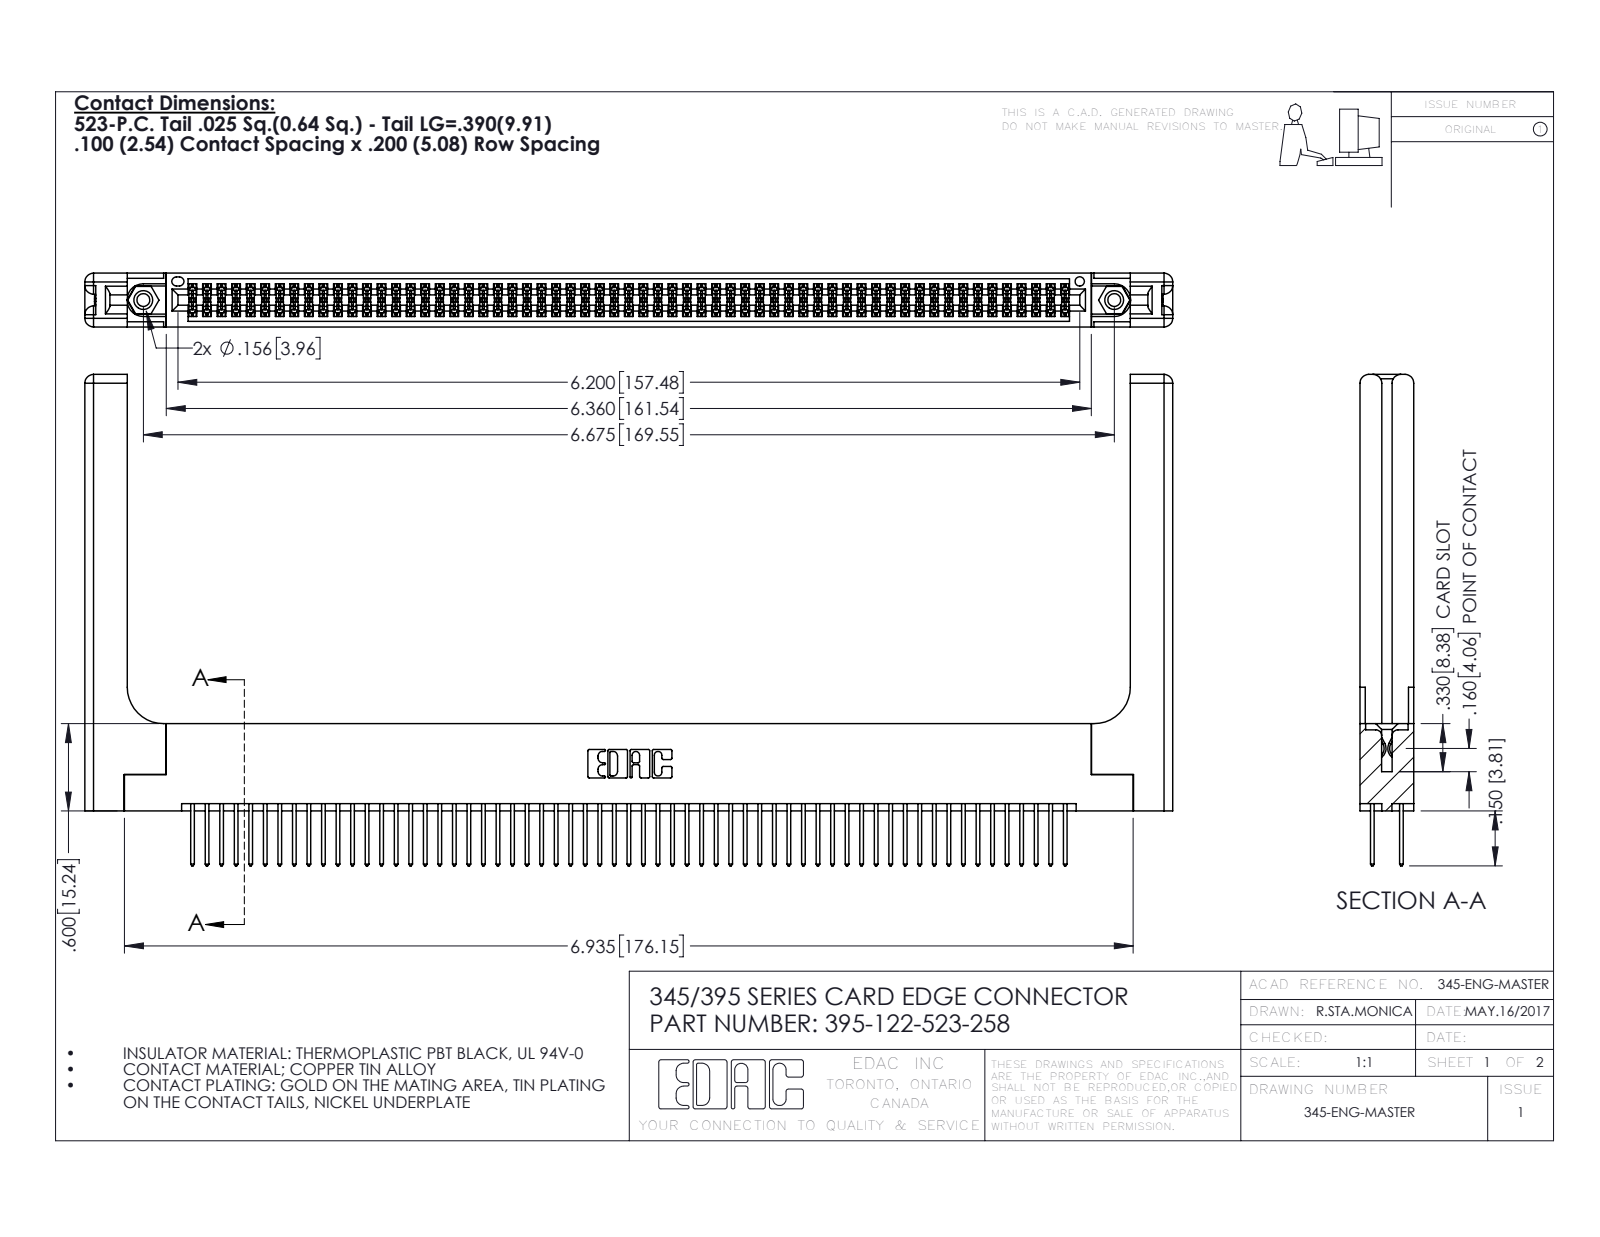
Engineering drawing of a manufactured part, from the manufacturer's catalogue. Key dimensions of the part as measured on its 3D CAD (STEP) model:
Part name (STEP PRODUCT): 345-292-001_345-293-123; 345 Part_Flush Mounting Lugs - 0.156 Dia-TH; 395-122-523-258; 345-220-058_345-220-058 (+1 more)
STEP written by: SolidWorks 2016 (CONFIG_CONTROL_DESIGN)
Units: inches
Bodies: 127 solids, 6482 faces (4254 planar, 2168 cylindrical, 60 other)
Overall size (bounding box): 7.479 × 3.377 × 0.37
Volume: 1.669 in³ · Surface area: 53.41 in²
Round holes (diameter × count): ⌀0.089 ×2, ⌀0.125 ×2, ⌀0.156 ×2, ⌀0.064 ×1
Round bosses / shafts (diameter × count): ⌀0.155 ×2
Partial cylindrical surfaces — rounded edges, fillets, slot ends (radius × count): R0.006 ×183, R0.01 ×122, R0.01 ×22, R0.06 ×16, R0.007 ×6, R0.031 ×6, R0.026 ×3, R0.014 ×2
Main face-to-face distances: 0.072, 0.298, 0.37, 0.2, 0.098, 0.272, 0.025, 0.225, 0.175, 0.148
Hole centre spacings: 0.27, 6.439, 6.675
